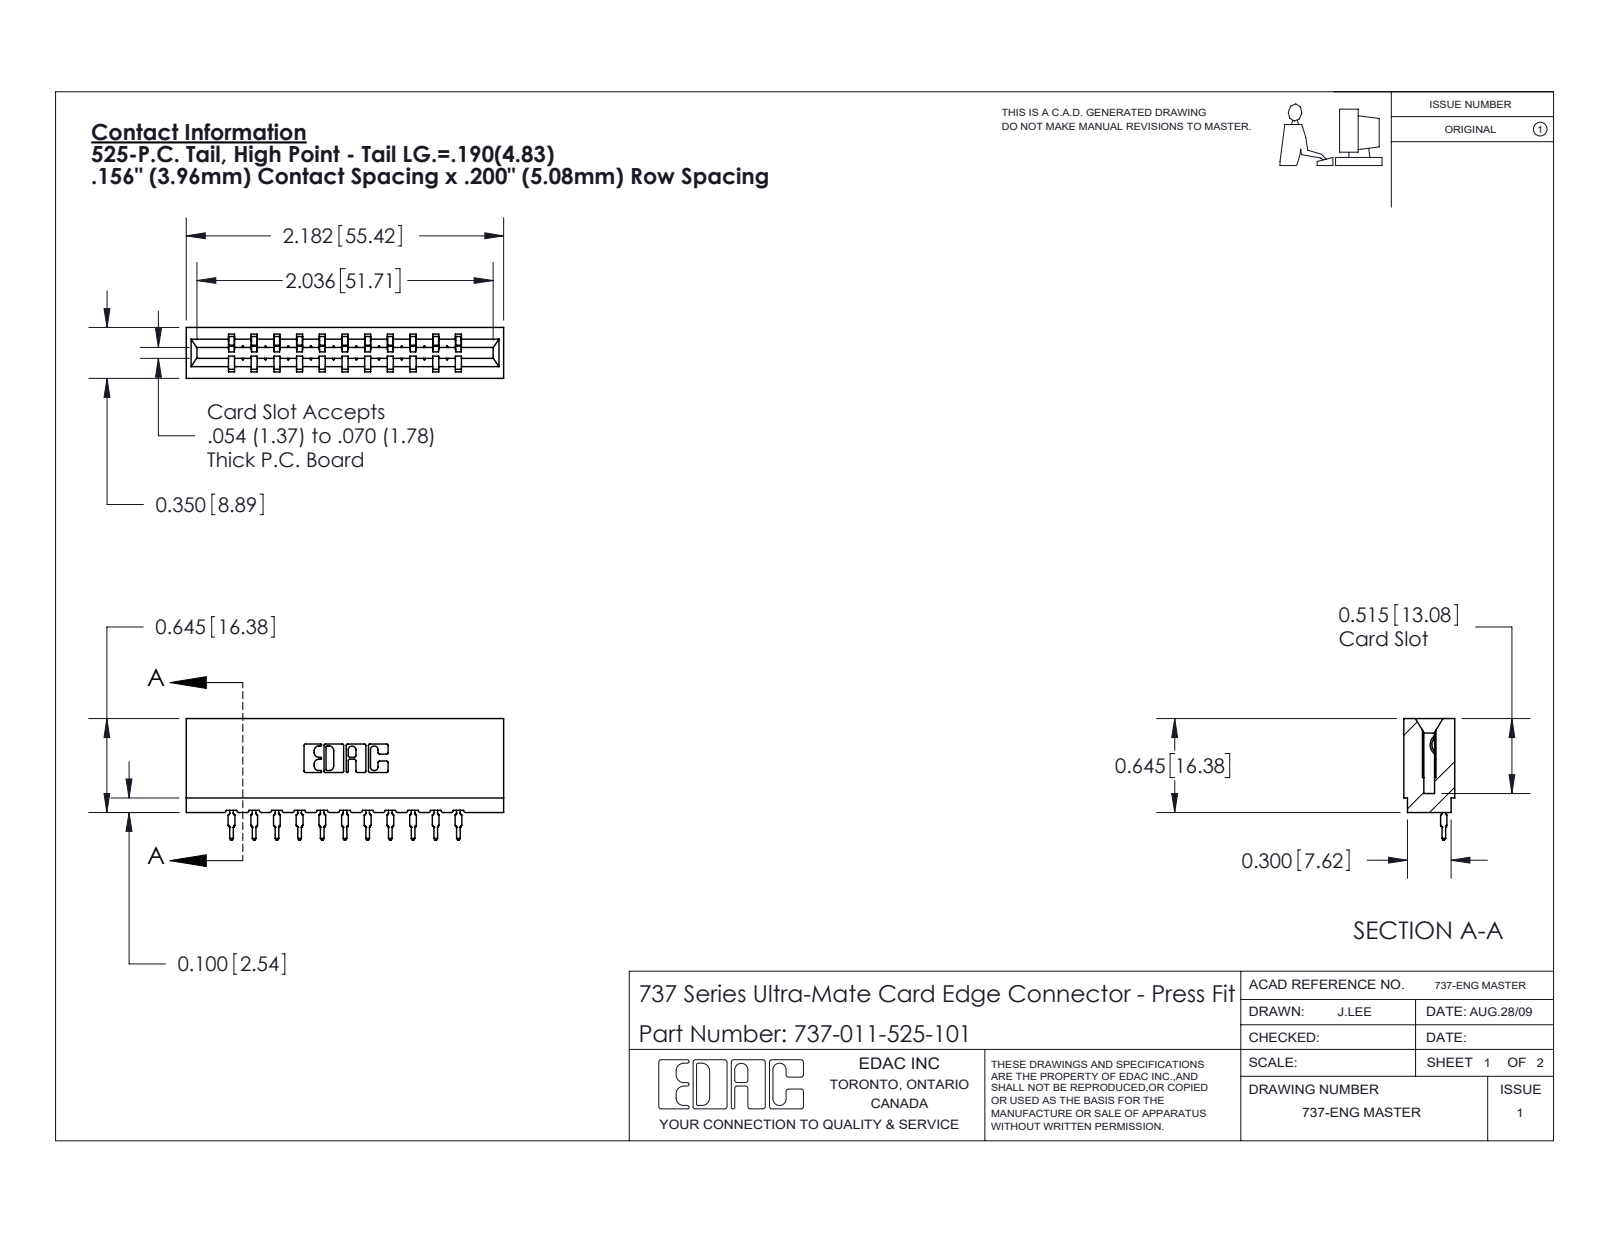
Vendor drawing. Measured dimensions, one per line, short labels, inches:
name: 745-292-001_525; 737-011-525-101; 737 Part_Insulator Option - 01
written by: SolidWorks 2020 (CONFIG_CONTROL_DESIGN)
unit: in
bodies: 12 solids, 1337 faces (802 planar, 249 cylindrical, 286 other)
size: 2.182 × 0.836 × 0.35
volume: 0.34 in³; area: 10.65 in²
rounds: 22× R0.01, 22× R0.015, 22× R0.021, 6× R0.007, 6× R0.031, 4× R0.005, 4× R0.011, 3× R0.026
face distances: 0.138, 0.212, 0.156, 0.35, 0.624, 0.312, 0.468, 0.78, 0.27, 0.354
